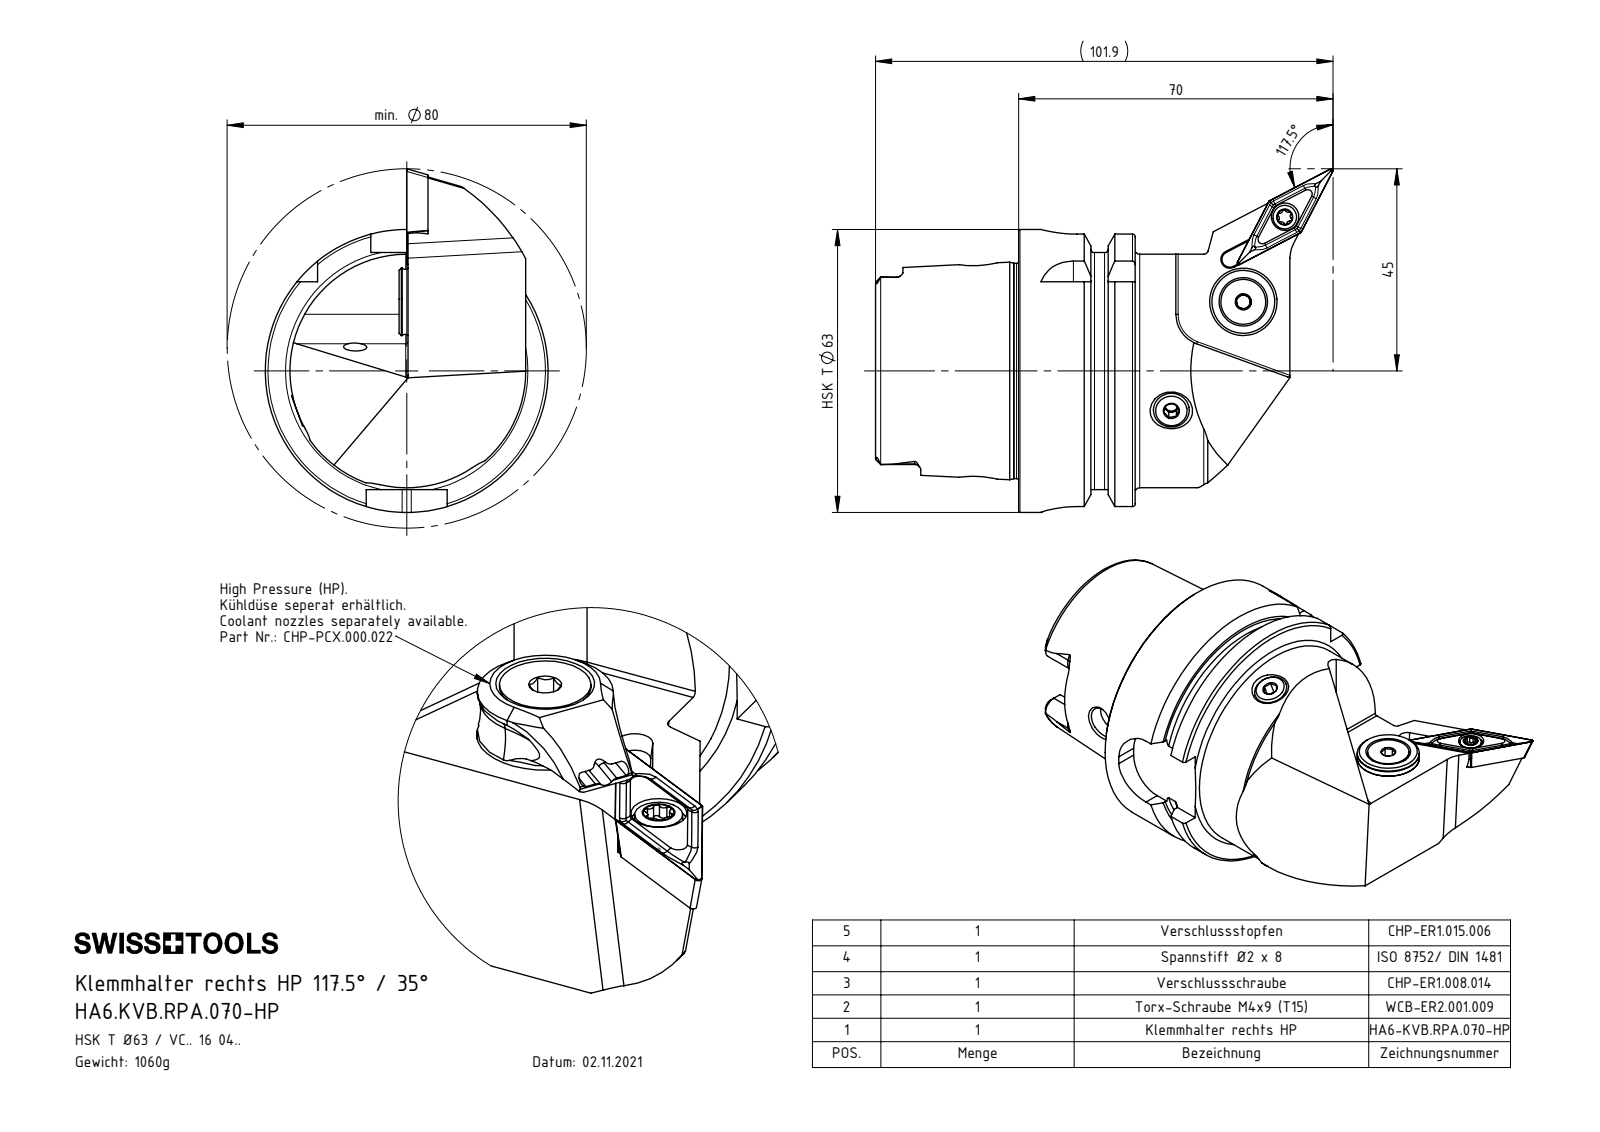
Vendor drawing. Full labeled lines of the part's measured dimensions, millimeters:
Part name (STEP PRODUCT): CHP-ER1.015.006; DIN 3771 - 13x1; HA6-KVB.RPA.070-HP_A; KV..RPA.070-HP (+6 more)
STEP written by: SolidWorks 2022 (AUTOMOTIVE_DESIGN)
Units: millimetres
Bodies: 8 solids, 422 faces (121 planar, 120 cylindrical, 181 other)
Overall size (bounding box): 101.9 × 76.5 × 63
Volume: 134 869 mm³ · Surface area: 32 241 mm²
Round holes (diameter × count): ⌀4.2 ×2, ⌀5 ×2, ⌀1.2 ×1, ⌀2 ×1, ⌀2.5 ×1, ⌀3 ×1, ⌀3.3 ×1, ⌀4.4 ×1, ⌀5.2 ×1, ⌀6.1 ×1, ⌀7 ×1, ⌀7.5 ×1
Round bosses / shafts (diameter × count): ⌀63 ×1, ⌀54.95 ×1, ⌀52 ×1, ⌀47.94 ×1, ⌀15 ×1, ⌀13.4 ×1, ⌀10 ×1, ⌀8 ×1
Partial cylindrical surfaces — rounded edges, fillets, slot ends (radius × count): R0.34 ×6, R0.59 ×6, R1.4 ×6, R8 ×4, R0.5 ×2, R2.82 ×2, R2.88 ×2, R7 ×2
Main face-to-face distances: 25.95, 16, 9.95, 26.2, 31.9, 41.85, 57.85, 52.8, 21.8, 11.85
Hole centre spacings: 4.5, 17.3, 17.41, 21, 21.1, 45.7, 47.05, 62.49
